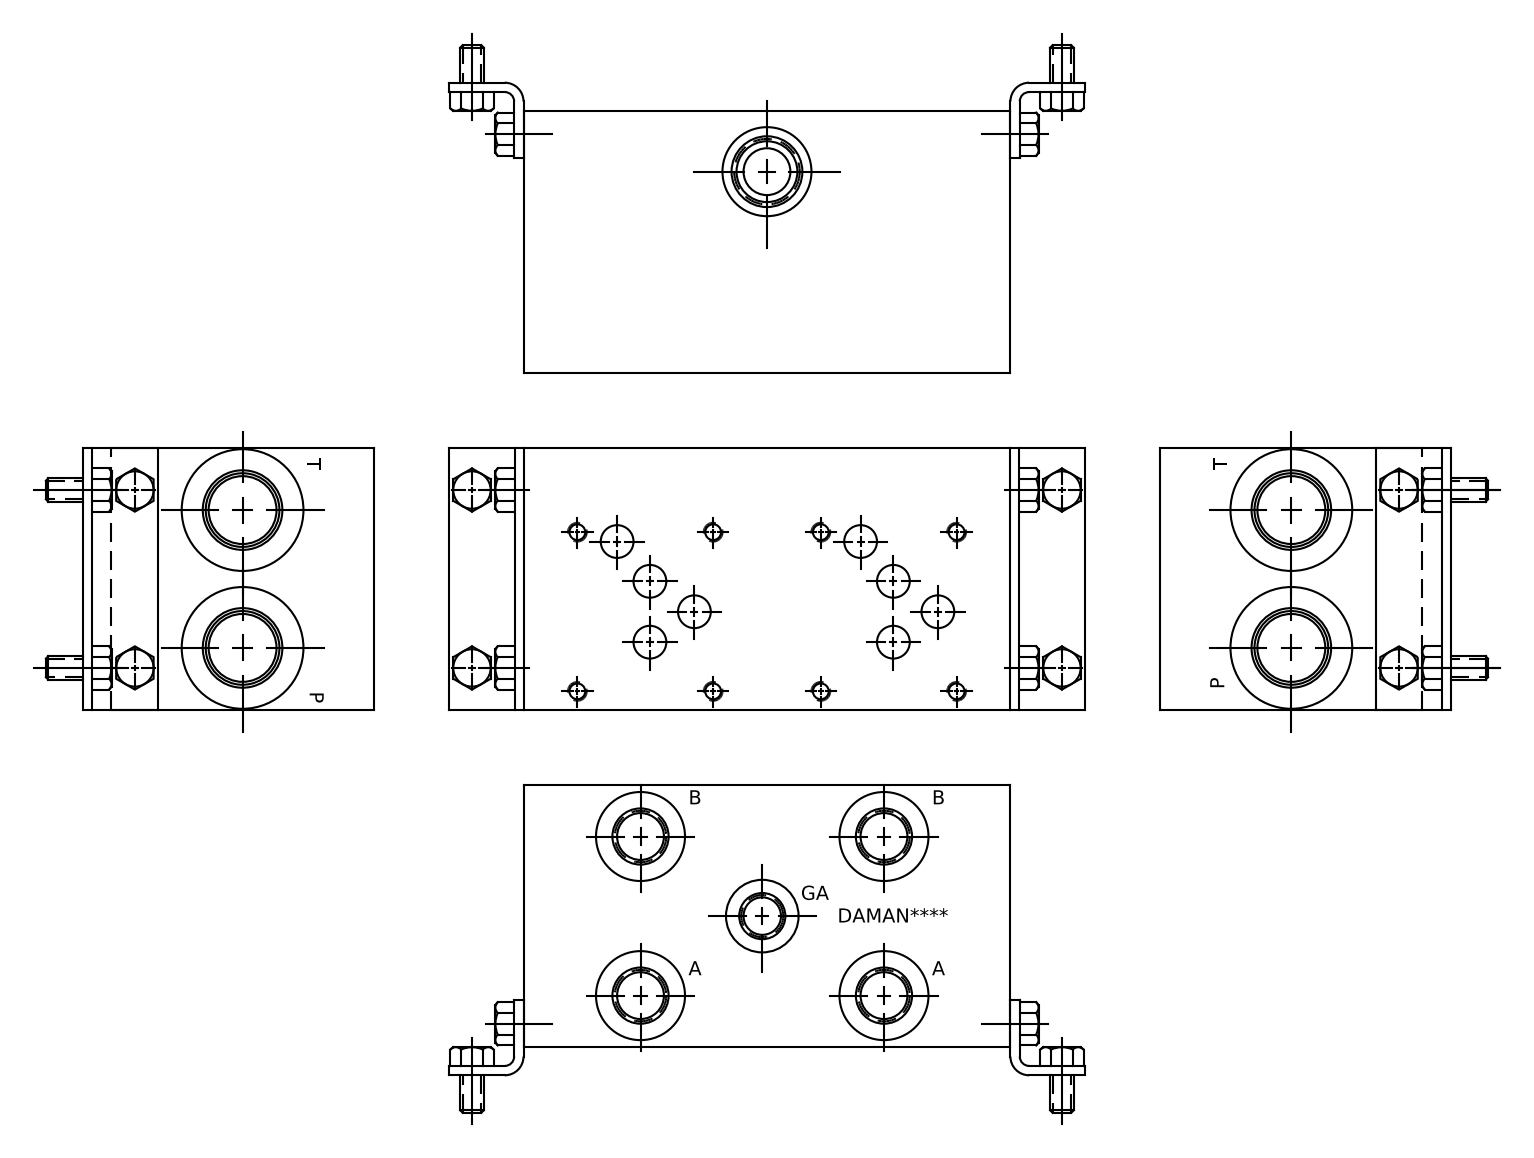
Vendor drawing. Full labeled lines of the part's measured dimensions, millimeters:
Part name (STEP PRODUCT): AD05P023S_C
STEP written by: Autodesk Inventor 2009 (AUTOMOTIVE_DESIGN)
Units: millimetres
Bodies: 1 solid, 202 faces (48 planar, 83 cylindrical, 71 other)
Overall size (bounding box): 165.1 × 88.9 × 88.9
Volume: 1 145 000 mm³ · Surface area: 107 094 mm²
Round holes (diameter × count): ⌀5.11 ×8, ⌀6.35 ×8, ⌀11.13 ×8, ⌀15.87 ×4, ⌀17.5 ×4, ⌀19.05 ×4, ⌀20.6 ×4, ⌀30.25 ×4, ⌀6.53 ×2, ⌀7.95 ×2, ⌀14.29 ×2, ⌀21.18 ×2
Main face-to-face distances: 88.9, 165.1, 0.76, 164.34, 88.14, 163.58, 3.33, 4.09, 161.01, 160.25
Hole centre spacings: 82.55, 43.02, 18.28, 27.16, 13.87, 17.48, 20.63, 27.72
